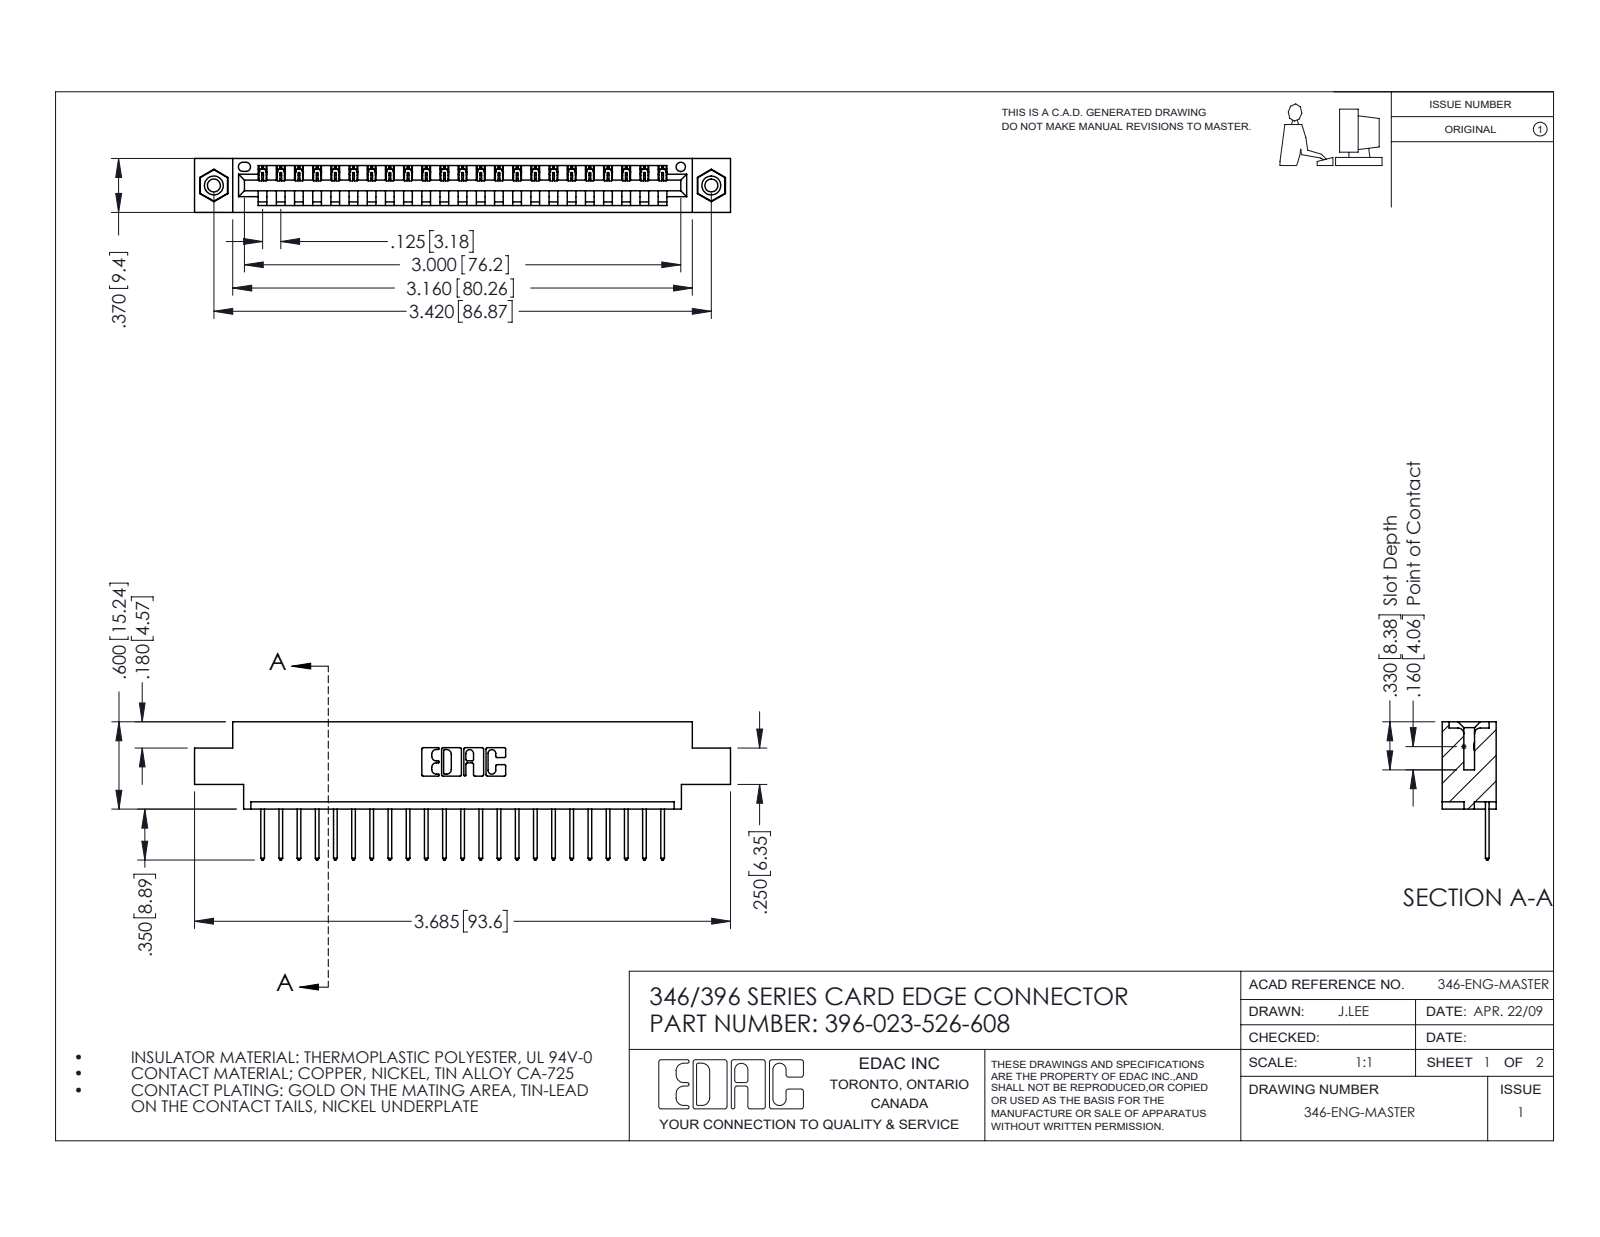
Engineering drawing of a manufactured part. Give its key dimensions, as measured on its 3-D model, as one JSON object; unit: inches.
{"part_name": "396-023-526-608; 345-292-001_345-293-126; 345-250-001_345-250-003-102; 346 Part_0.170 Offset - 0.156 Dia-TI", "step_written_by": "SolidWorks 2016 (CONFIG_CONTROL_DESIGN)", "units": "inches", "bodies": {"solids": 26, "faces": 1520, "planar": 1032, "cylindrical": 472, "other": 16}, "overall_size": [3.685, 0.95, 0.37], "volume_in3": 0.528, "surface_area_in2": 16.69, "round_holes": [[0.089, 2], [0.125, 2], [0.156, 2], [0.064, 1]], "round_bosses_or_shafts": [[0.155, 2]], "partial_cylinders_radius": [[0.006, 46], [0.01, 46], [0.01, 22], [0.007, 6], [0.031, 6], [0.026, 3], [0.031, 2], [0.04, 2]], "face_to_face_distances": [0.048, 0.322, 0.37, 0.25, 0.072, 0.298, 0.025, 0.222, 0.148, 0.1], "hole_center_spacings": [0.246, 3.212, 3.42]}
